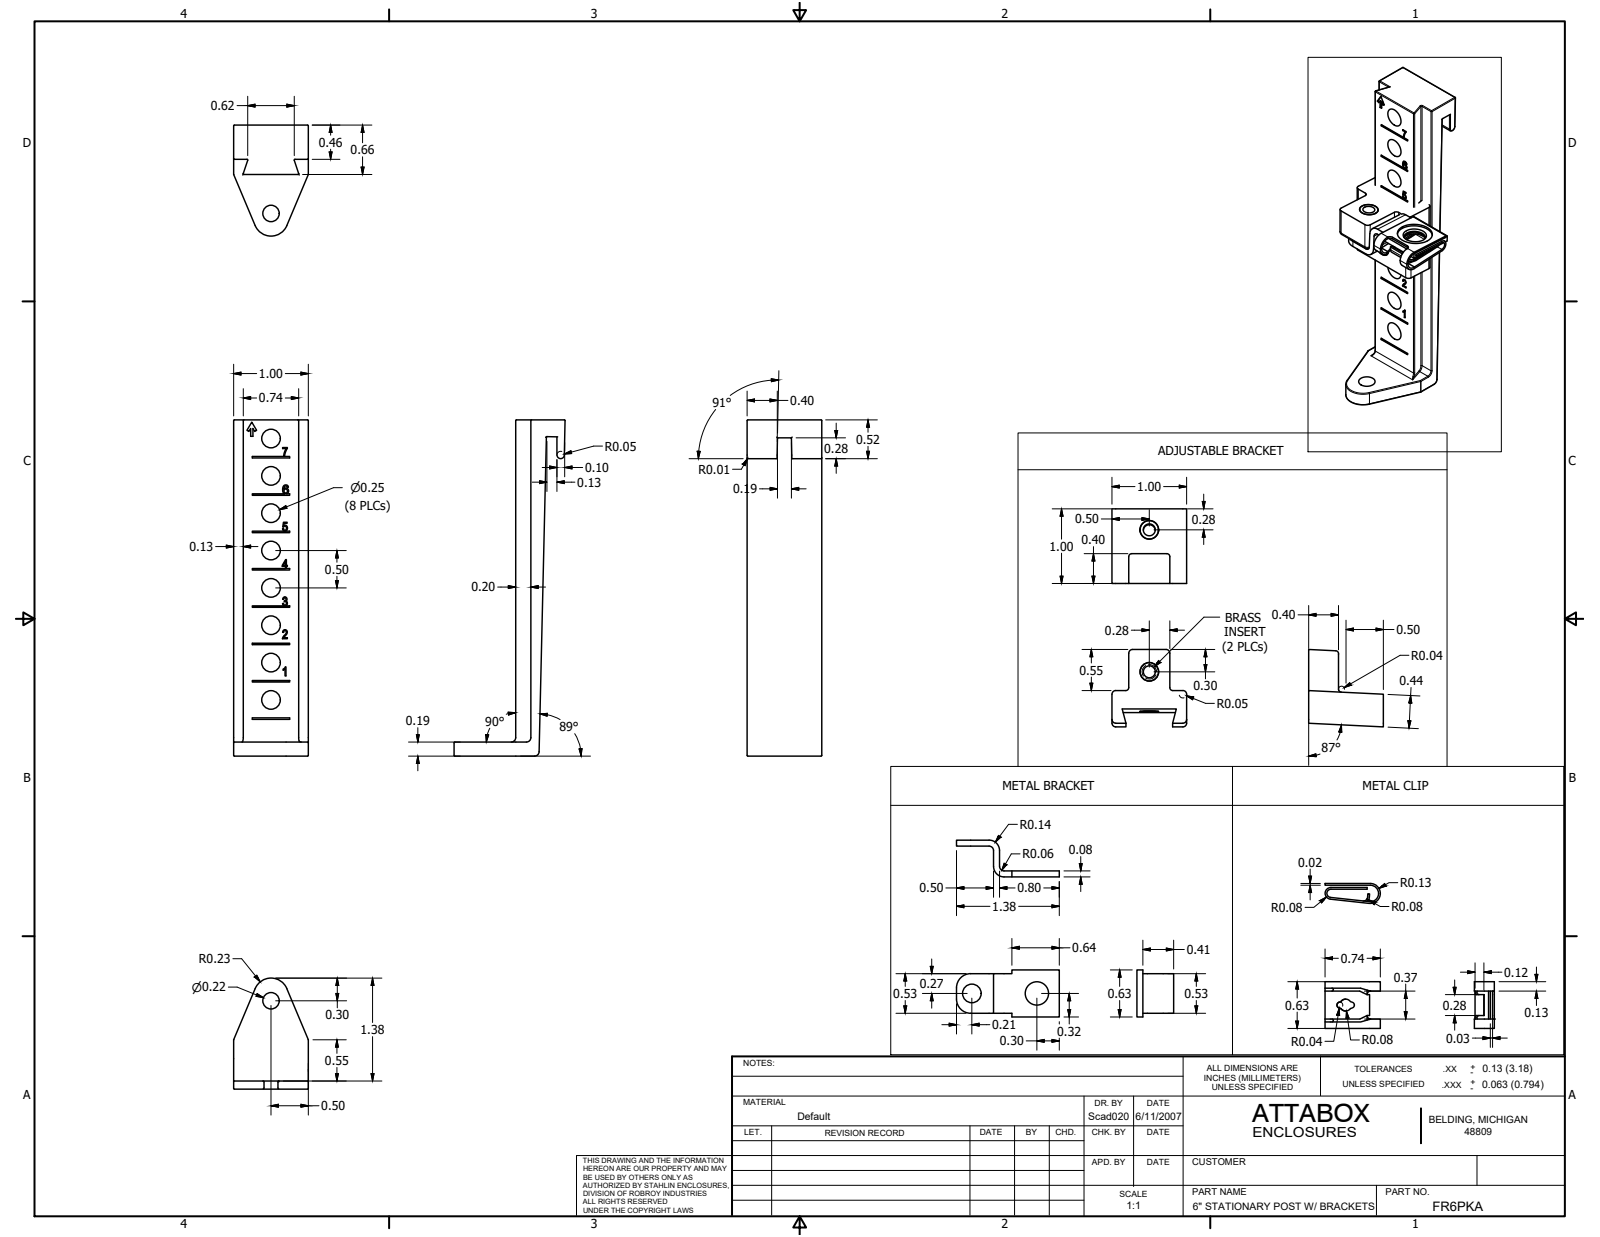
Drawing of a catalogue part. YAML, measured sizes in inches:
part_name: "FR6PKA"
step_written_by: "SolidWorks 2019 (AUTOMOTIVE_DESIGN)"
units: inches
bodies: {solids: 25, faces: 1384, planar: 682, cylindrical: 318, other: 384}
overall_size: [10.622, 8.622, 4.703]
volume: 7.736
surface_area: 102.8
round_holes:
  - {diameter: 0.25, count: 32}
  - {diameter: 0.253, count: 8}
  - {diameter: 0.217, count: 4}
  - {diameter: 0.22, count: 4}
  - {diameter: 0.156, count: 1}
round_bosses_or_shafts:
  - {diameter: 0.19, count: 12}
  - {diameter: 0.373, count: 8}
  - {diameter: 0.433, count: 4}
  - {diameter: 0.315, count: 4}
  - {diameter: 0.246, count: 1}
partial_cylinders:
  - {radius: 0.01, count: 170}
  - {radius: 0.06, count: 56}
  - {radius: 0.049, count: 4}
  - {radius: 0.23, count: 4}
face_to_face_distances: [11.295, 1.415, 6.855, 4.441, 5.44, 5.855, 1, 0.203, 4.643, 5.643]
hole_center_spacings: [1.5, 0.5, 1, 1.732, 2.061, 1.414, 2, 2.45]
